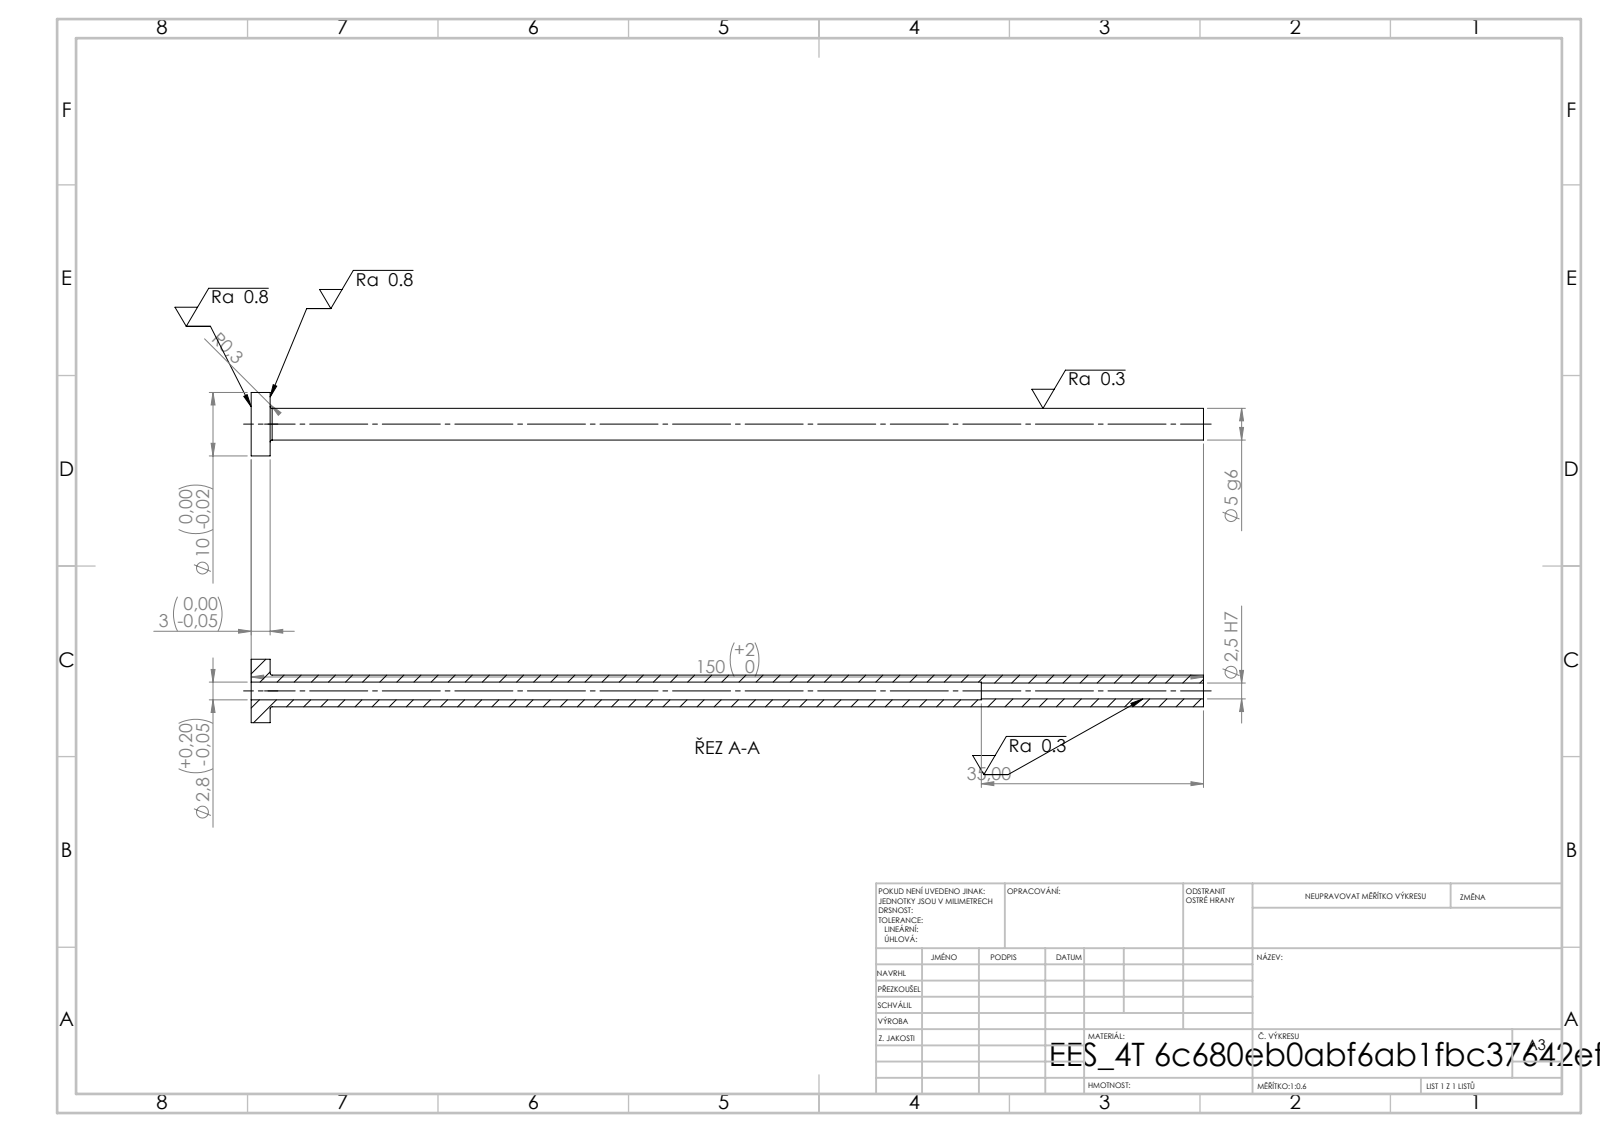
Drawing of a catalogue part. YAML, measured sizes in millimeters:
step_written_by: "SolidWorks 2019 (CONFIG_CONTROL_DESIGN)"
units: millimeters
bodies: {solids: 1, faces: 14, planar: 4, cylindrical: 8, other: 2}
overall_size: [150, 10, 10]
volume: 2242
surface_area: 3835
round_holes:
  - {diameter: 2.5, count: 1}
  - {diameter: 2.8, count: 1}
round_bosses_or_shafts:
  - {diameter: 10, count: 1}
  - {diameter: 5, count: 1}
face_to_face_distances: [3, 150, 147, 115, 112, 35]
